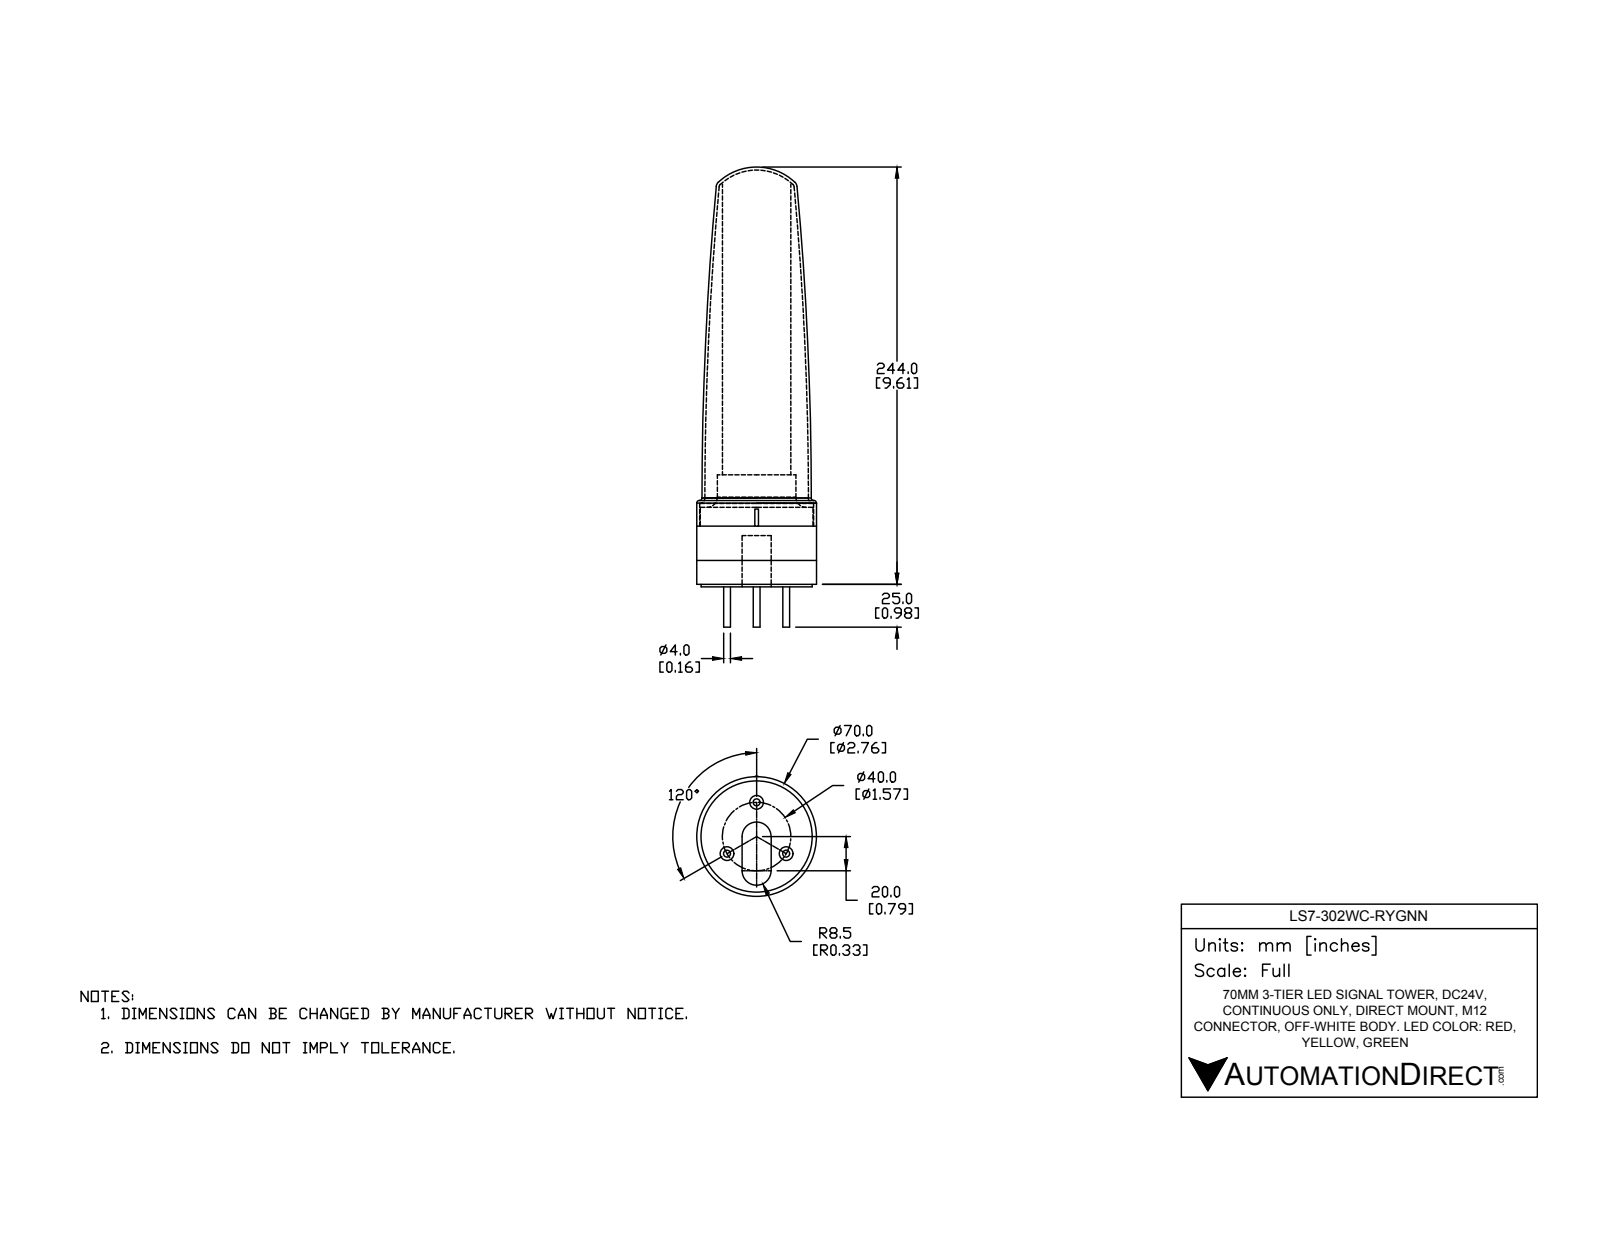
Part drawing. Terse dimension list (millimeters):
name: LS7-302WC-RYGNN
written by: SolidWorks 2016 (AUTOMOTIVE_DESIGN)
unit: mm
bodies: 8 solids, 84 faces (27 planar, 39 cylindrical, 18 other)
size: 269 × 70.3 × 70
volume: 468 745 mm³; area: 136 804 mm²
holes: 3× ⌀8, 1× ⌀66.6
bosses: 3× ⌀4, 1× ⌀70, 1× ⌀66, 1× ⌀65, 1× ⌀46, 1× ⌀40
rounds: 2× R8.5, 1× R1, 1× R2
face distances: 14, 64, 50, 15.5, 1.5, 65.5, 30, 35.5, 235.5, 234
hole spacings: 20, 34.64
